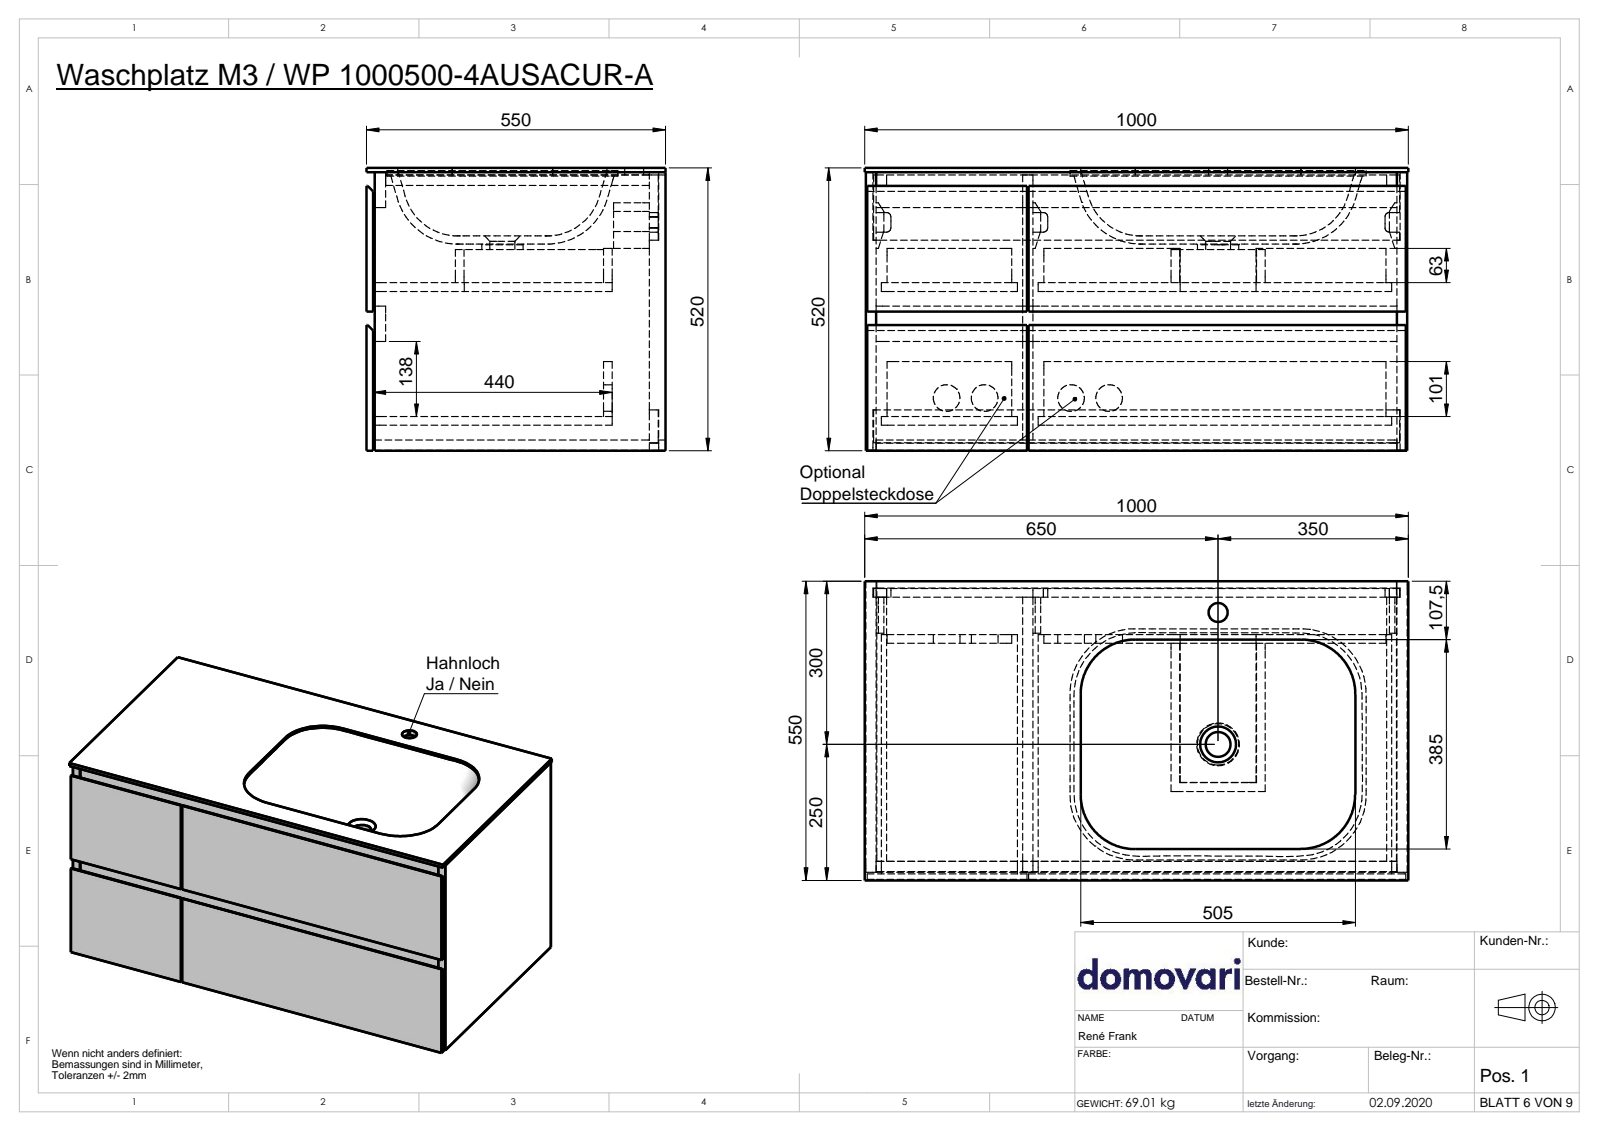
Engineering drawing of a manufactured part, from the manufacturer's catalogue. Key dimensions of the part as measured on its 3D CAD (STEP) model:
Part name (STEP PRODUCT): WP 1000500-4AUSACUR-A_us_Spanweiá lackiert<Wie bearbeitet>; WP 1000500-4AUSACUR-A_wt_Mit Hahnloch ohne berlauf; WP1000500-4AUSACUR-A
STEP written by: SolidWorks 2020 (AUTOMOTIVE_DESIGN)
Units: millimetres
Bodies: 31 solids, 285 faces (251 planar, 24 cylindrical, 10 other)
Overall size (bounding box): 1000 × 558 × 520
Volume: 61 050 000 mm³ · Surface area: 8 579 000 mm²
Round holes (diameter × count): ⌀49 ×4, ⌀35 ×1, ⌀46 ×1
Round bosses / shafts (diameter × count): ⌀76 ×1
Partial cylindrical surfaces — rounded edges, fillets, slot ends (radius × count): R8 ×6, R100 ×4
Main face-to-face distances: 19, 16, 246, 977, 288.5, 688.5, 12, 27, 43, 62
Hole centre spacings: 70, 229, 159, 242.5, 299
